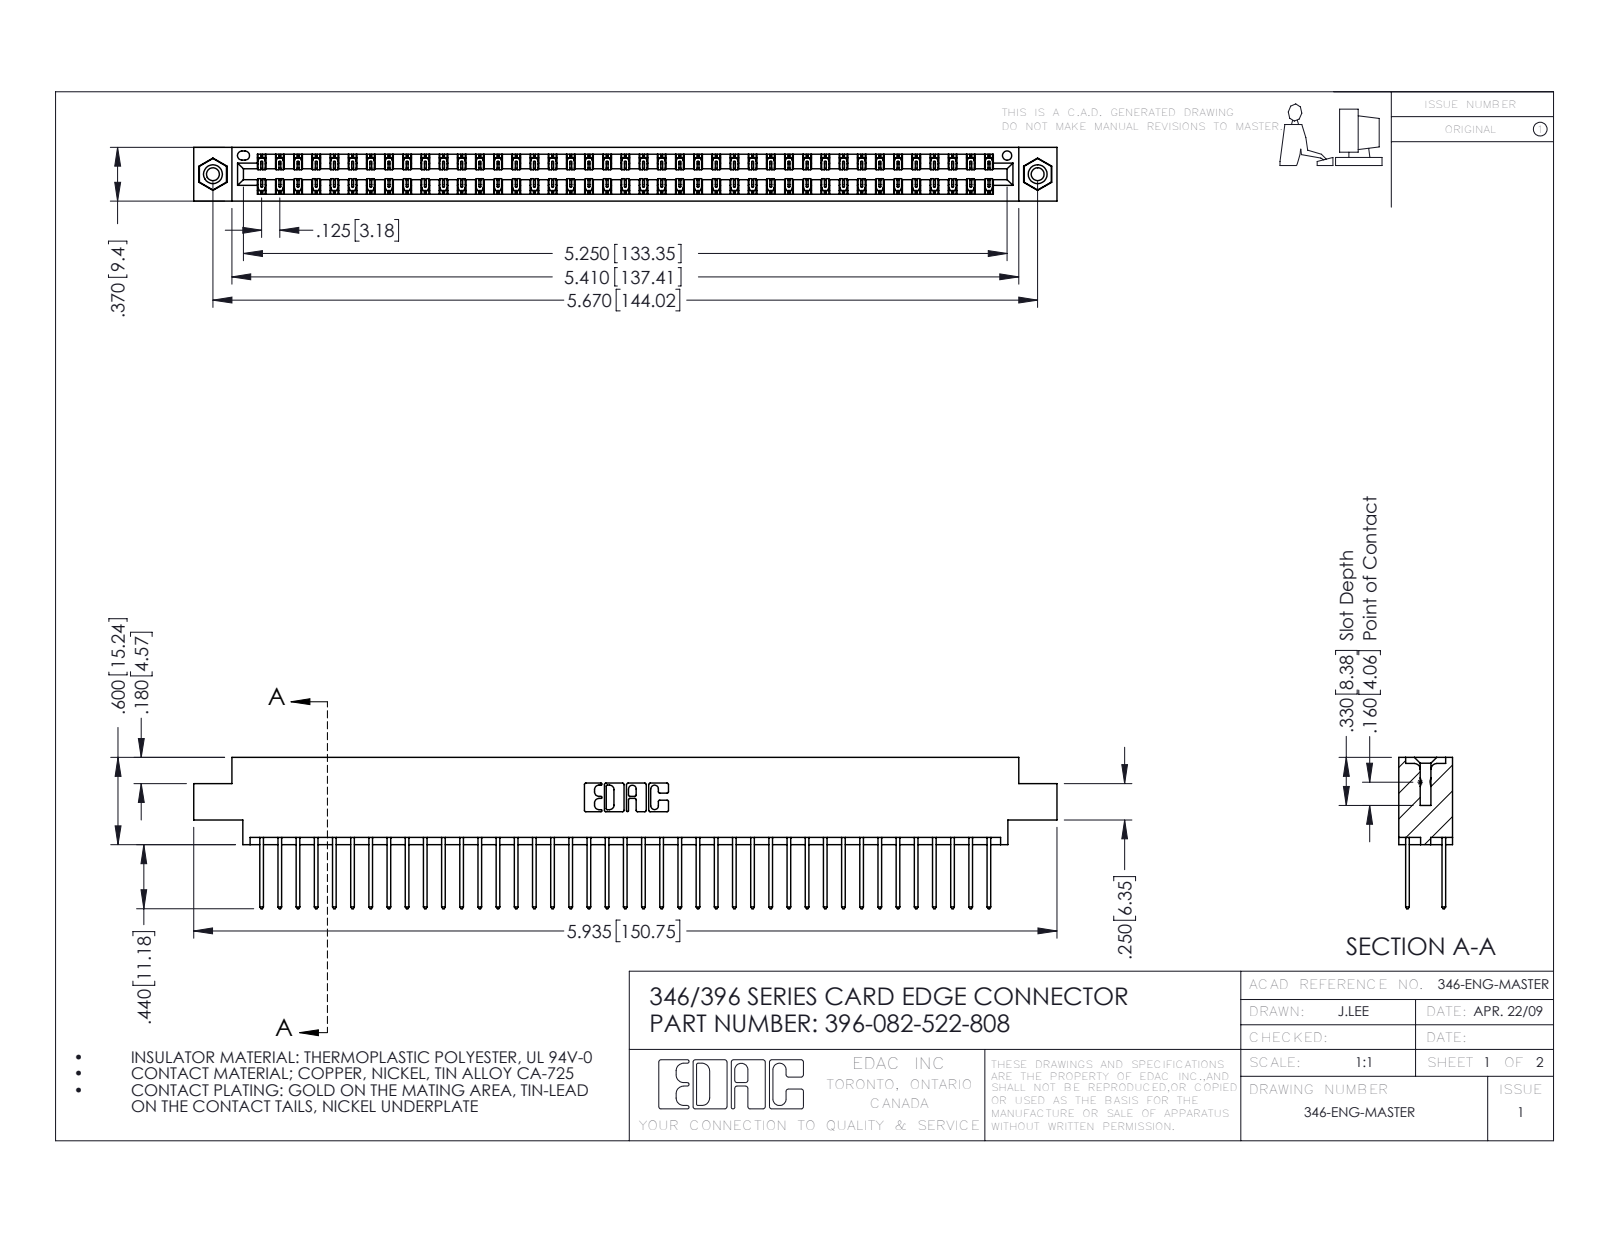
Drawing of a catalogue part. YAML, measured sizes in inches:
part_name: "396-082-522-808; 345-292-001_345-293-122; 345-250-001_345-250-003-102; 346 Part_0.170 Offset - 0.156 Dia-TI"
step_written_by: "SolidWorks 2016 (CONFIG_CONTROL_DESIGN)"
units: inches
bodies: {solids: 85, faces: 4450, planar: 2982, cylindrical: 1452, other: 16}
overall_size: [5.935, 1.04, 0.37]
volume: 0.9
surface_area: 33.2
round_holes:
  - {diameter: 0.089, count: 2}
  - {diameter: 0.125, count: 2}
  - {diameter: 0.156, count: 2}
  - {diameter: 0.064, count: 1}
round_bosses_or_shafts:
  - {diameter: 0.155, count: 2}
partial_cylinders:
  - {radius: 0.006, count: 123}
  - {radius: 0.01, count: 82}
  - {radius: 0.01, count: 22}
  - {radius: 0.007, count: 6}
  - {radius: 0.031, count: 6}
  - {radius: 0.026, count: 3}
  - {radius: 0.014, count: 2}
  - {radius: 0.022, count: 2}
face_to_face_distances: [0.048, 0.322, 0.25, 0.37, 0.072, 0.298, 0.025, 0.275, 0.222, 0.148]
hole_center_spacings: [0.246, 5.461, 5.67]
